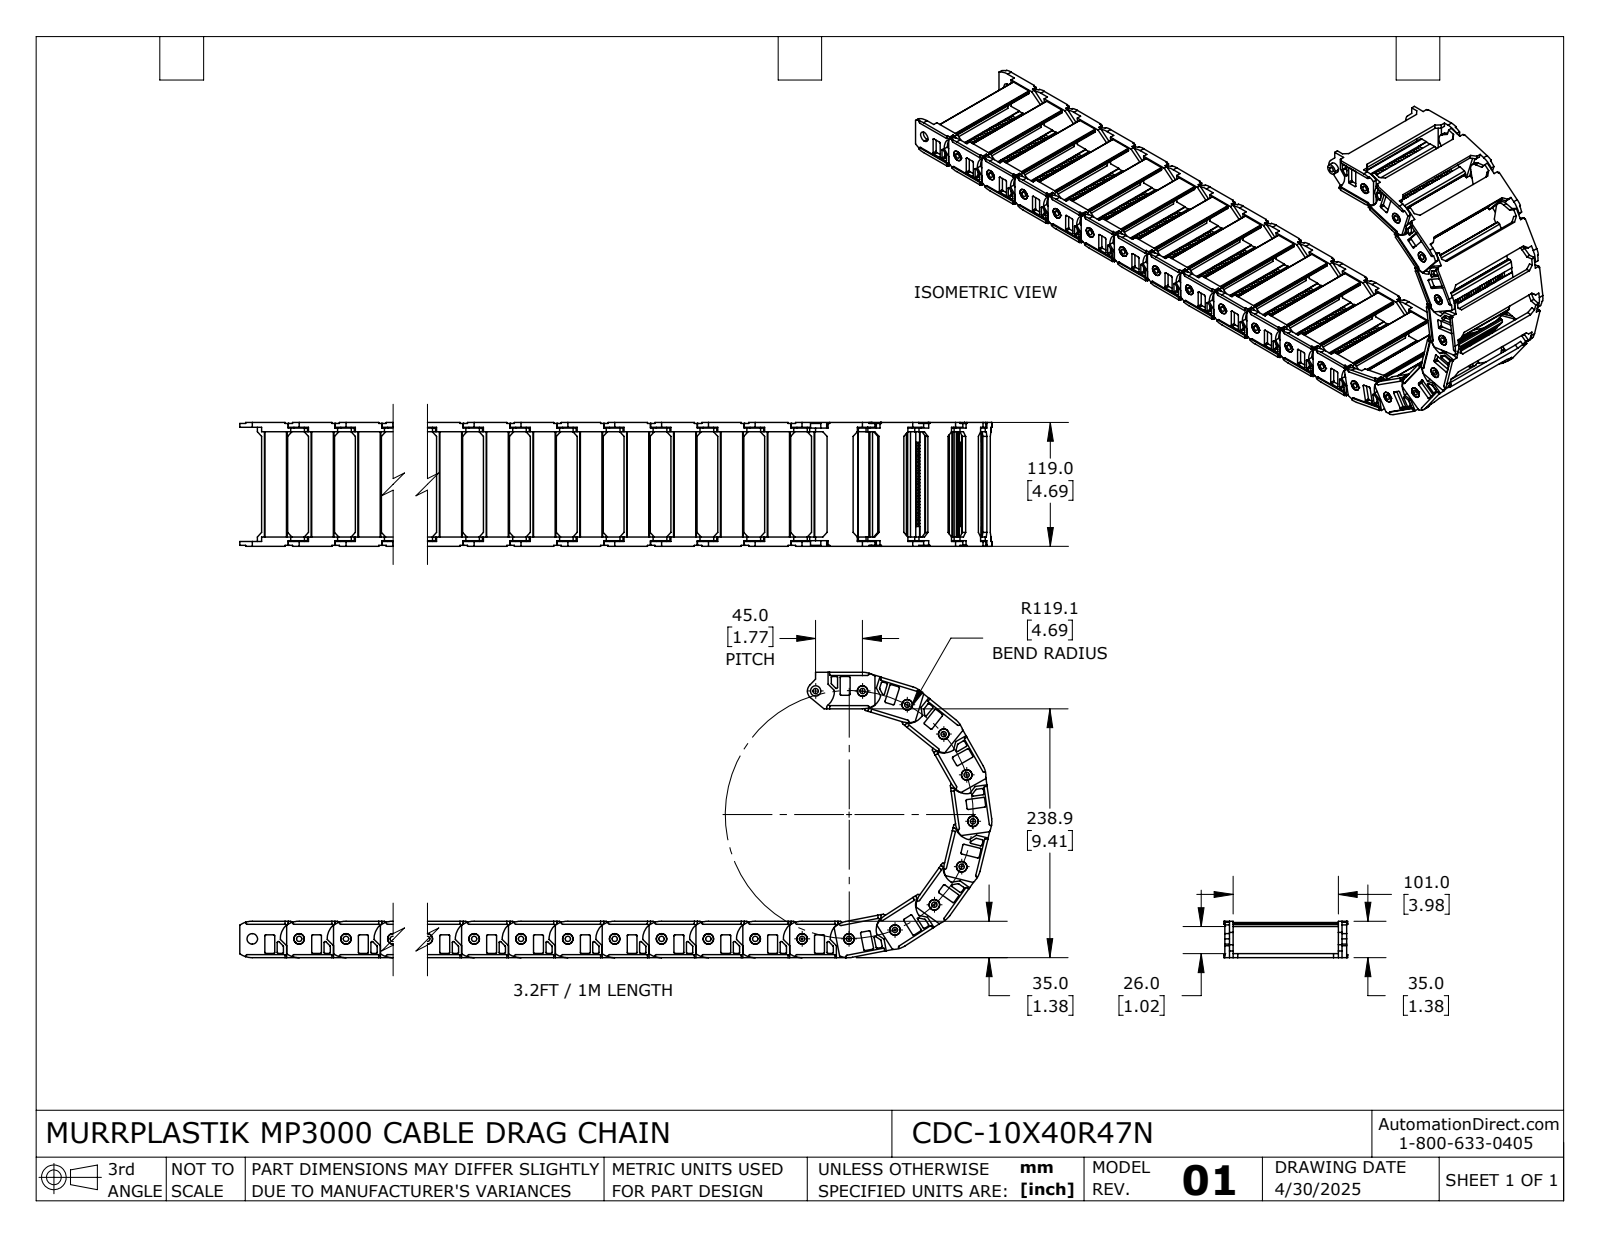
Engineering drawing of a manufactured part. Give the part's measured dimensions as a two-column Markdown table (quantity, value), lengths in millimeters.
| quantity | value |
| --- | --- |
| part name | CDC-10X40R47N |
| STEP written by | SolidWorks 2024 (AUTOMOTIVE_DESIGN) |
| units | millimeters |
| bodies | 22 solids, 5456 faces (4356 planar, 1100 cylindrical, 0 other) |
| overall size | 734.23 × 274 × 119 |
| volume | 824 420 mm³ |
| surface area | 512 256 mm² |
| round holes (diameter × count) | 5.1 × 22, 10.1 × 22 |
| round bosses / shafts (diameter × count) | 10 × 22 |
| partial cylindrical surfaces (radius × count) | 1 × 176, 0.5 × 88, 1.5 × 44, 2 × 44, 21 × 44, 2.8 × 22, 8 × 22, 18 × 22 |
| main face-to-face distances | 109, 4, 8, 33.8, 3.8, 30, 3.7, 113.3, 4.3, 105.3 |
| hole center spacings | 45, 90, 135, 180, 225, 270, 315, 360 |
